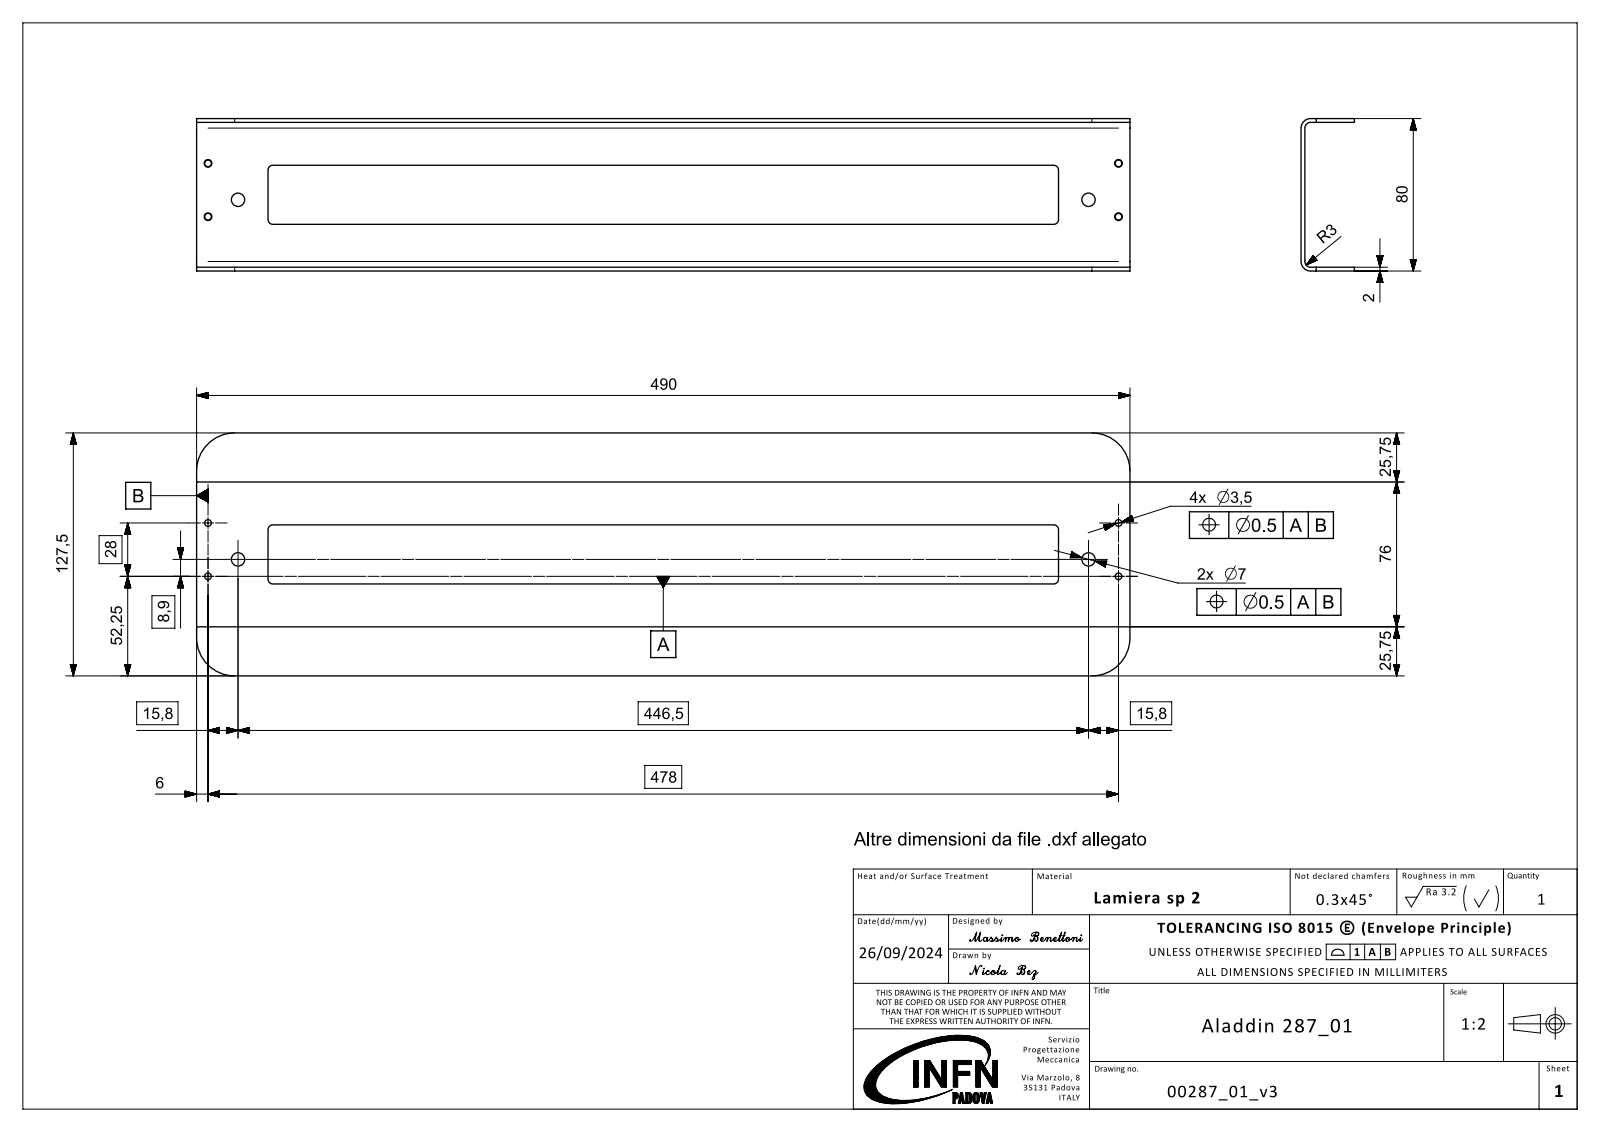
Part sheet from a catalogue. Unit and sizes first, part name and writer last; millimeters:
Units: millimetres
Overall size (bounding box): 490 × 80 × 28
Round holes (diameter × count): ⌀3.5 ×4, ⌀7 ×2
Partial cylindrical surfaces — rounded edges, fillets, slot ends (radius × count): R2.5 ×4, R3 ×2, R5 ×2, R20 ×2
Main face-to-face distances: 2, 78, 80, 76, 26, 28, 24.5, 55.5, 22.5, 53.5
Hole centre spacings: 18.09, 24.76, 28, 462.34, 462.64, 478, 478.82, 446.5
Volume: 99 355 mm³ · Surface area: 103 703 mm²
Bodies: 1 solid, 40 faces (14 planar, 18 cylindrical, 8 other)
Part name (STEP PRODUCT): 00287_01_v3_objects
STEP written by: SIEMENS PLM Software NX2306.9102 (AUTOMOTIVE_DESIGN)
